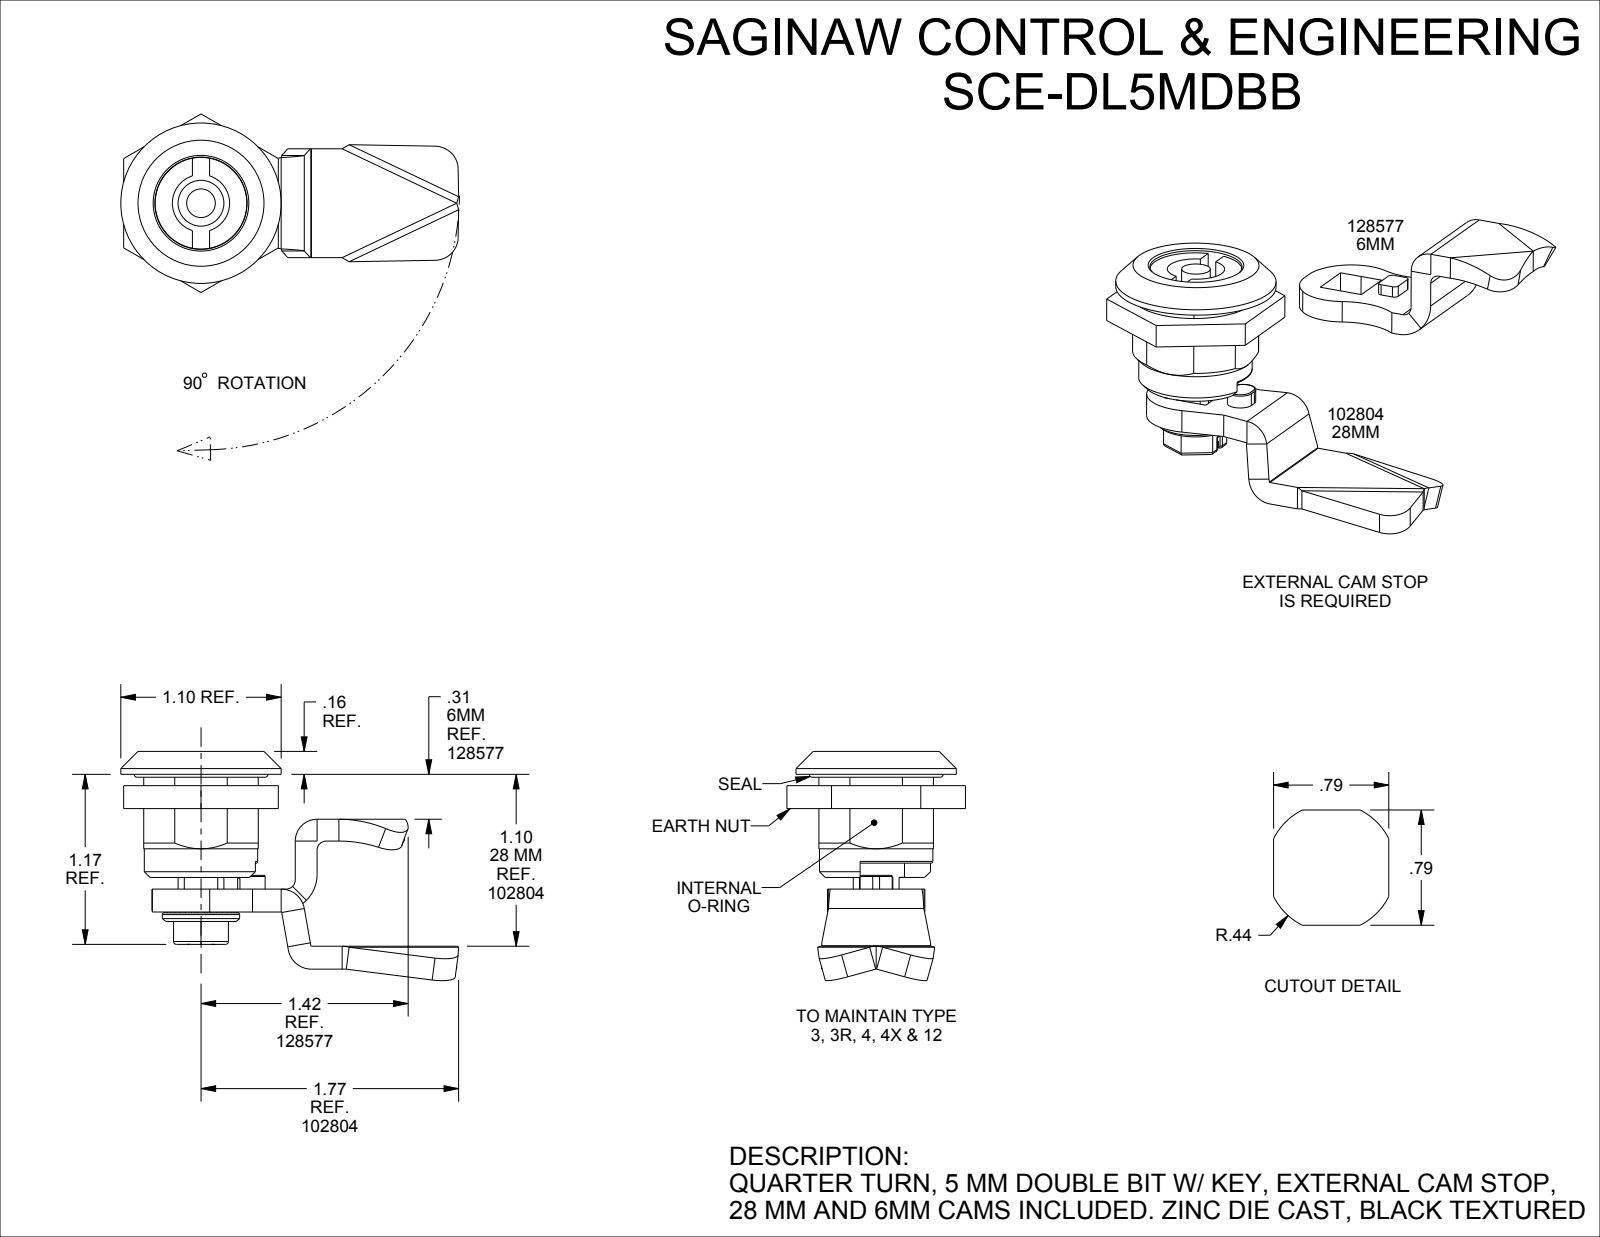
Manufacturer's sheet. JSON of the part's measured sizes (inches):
{"part_name": "SCE-DL5MDB", "step_written_by": "SolidWorks 2021 (AUTOMOTIVE_DESIGN)", "units": "inches", "bodies": {"solids": 8, "faces": 325, "planar": 142, "cylindrical": 118, "other": 65}, "overall_size": [3.426, 2.829, 2.288], "volume_in3": 0.984, "surface_area_in2": 19.65, "round_holes": [[0.197, 1], [0.315, 1], [0.394, 1], [0.634, 1], [0.799, 1]], "round_bosses_or_shafts": [[1.102, 1], [0.78, 1], [0.63, 1], [0.531, 1], [0.504, 1], [0.39, 1], [0.217, 1]], "partial_cylinders_radius": [[0.012, 30], [0.02, 12], [0.03, 4], [0.157, 4], [0.3, 4], [0.004, 2], [0.008, 2], [0.087, 2]], "face_to_face_distances": [0.157, 1.103, 0.711, 0.393, 0.15, 0.235, 1.339, 0.553, 0.946, 0.4]}
